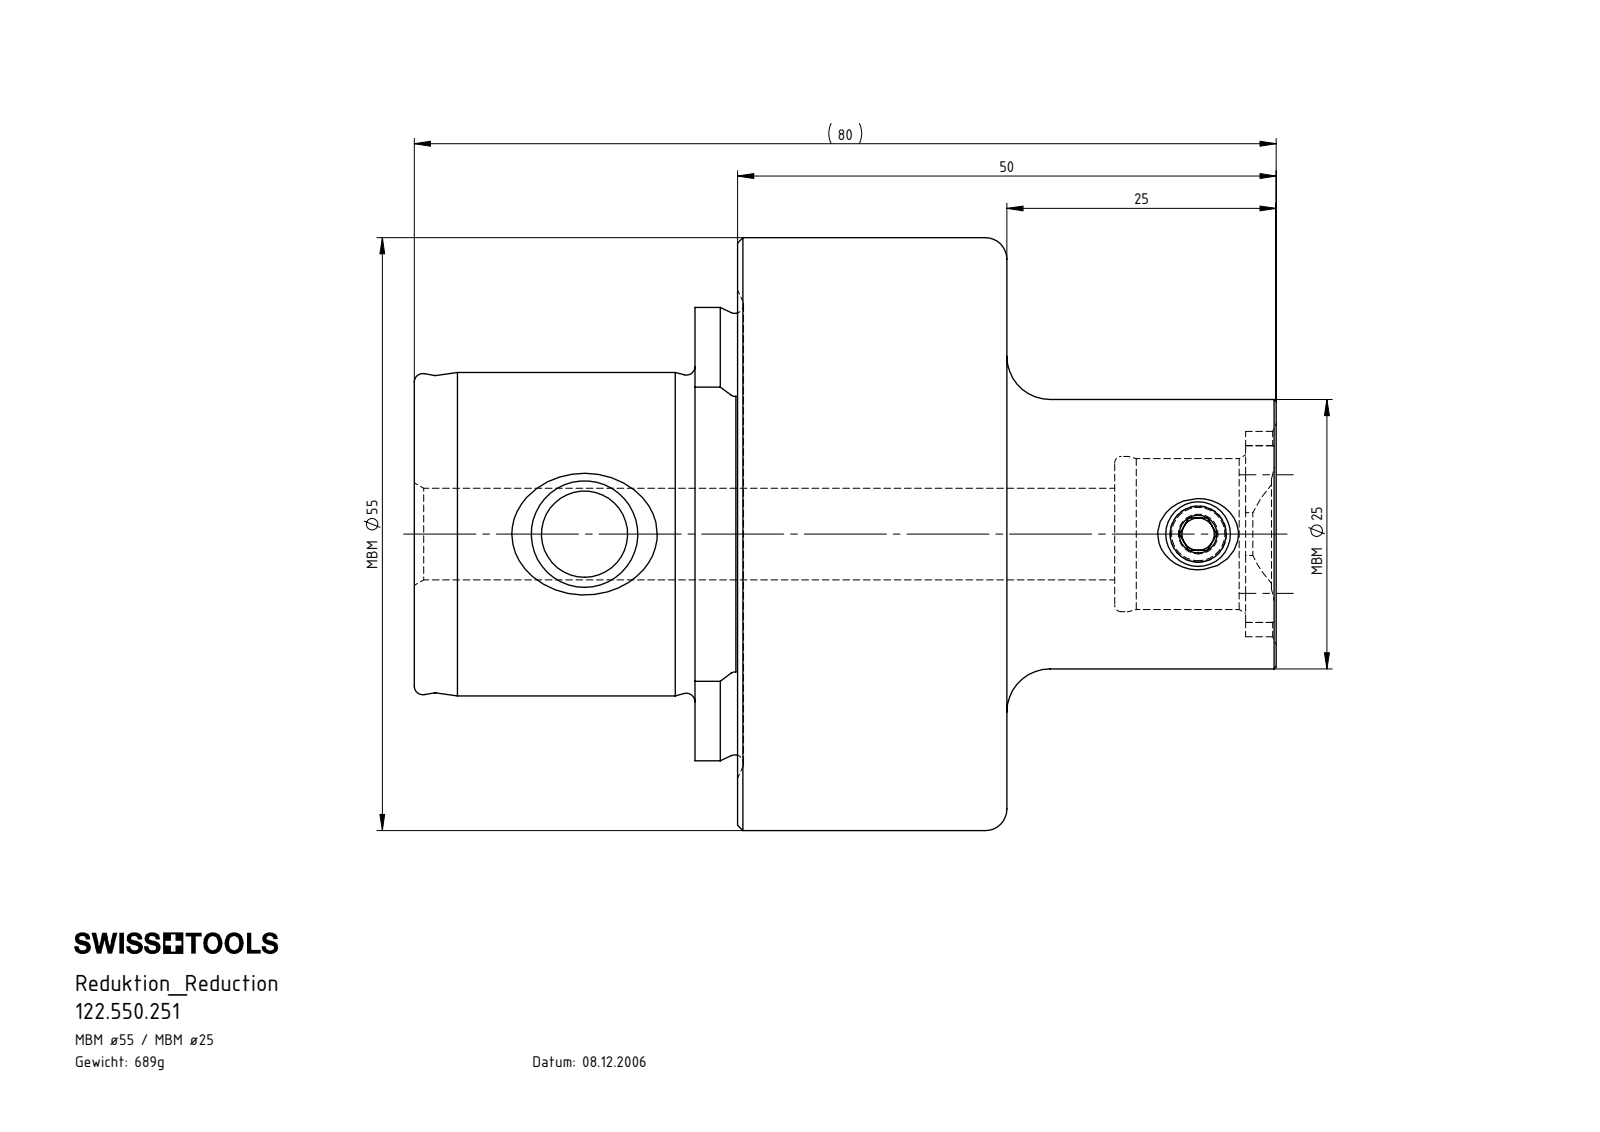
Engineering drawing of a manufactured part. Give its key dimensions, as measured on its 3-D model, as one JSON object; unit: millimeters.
{"part_name": "MB2-ER1.001.008_A; 122.550.251; MB5-MB2.K01.050_C", "step_written_by": "SolidWorks 2017 (CONFIG_CONTROL_DESIGN)", "units": "millimeters", "bodies": {"solids": 2, "faces": 132, "planar": 31, "cylindrical": 34, "other": 67}, "overall_size": [80, 55, 55], "volume_mm3": 87708, "surface_area_mm2": 16379, "round_holes": [[3, 1], [5.25, 1], [8, 1], [8.5, 1], [14, 1], [14.4, 1]], "round_bosses_or_shafts": [[55, 1], [30, 1], [25, 1], [6, 1]], "partial_cylinders_radius": [[2.7, 4], [8, 1], [9.53, 1], [21.02, 1]], "face_to_face_distances": [25, 30, 55, 26.05, 3.95, 28.95, 29.85, 3.8, 25.15, 80], "hole_center_spacings": [56.95]}
